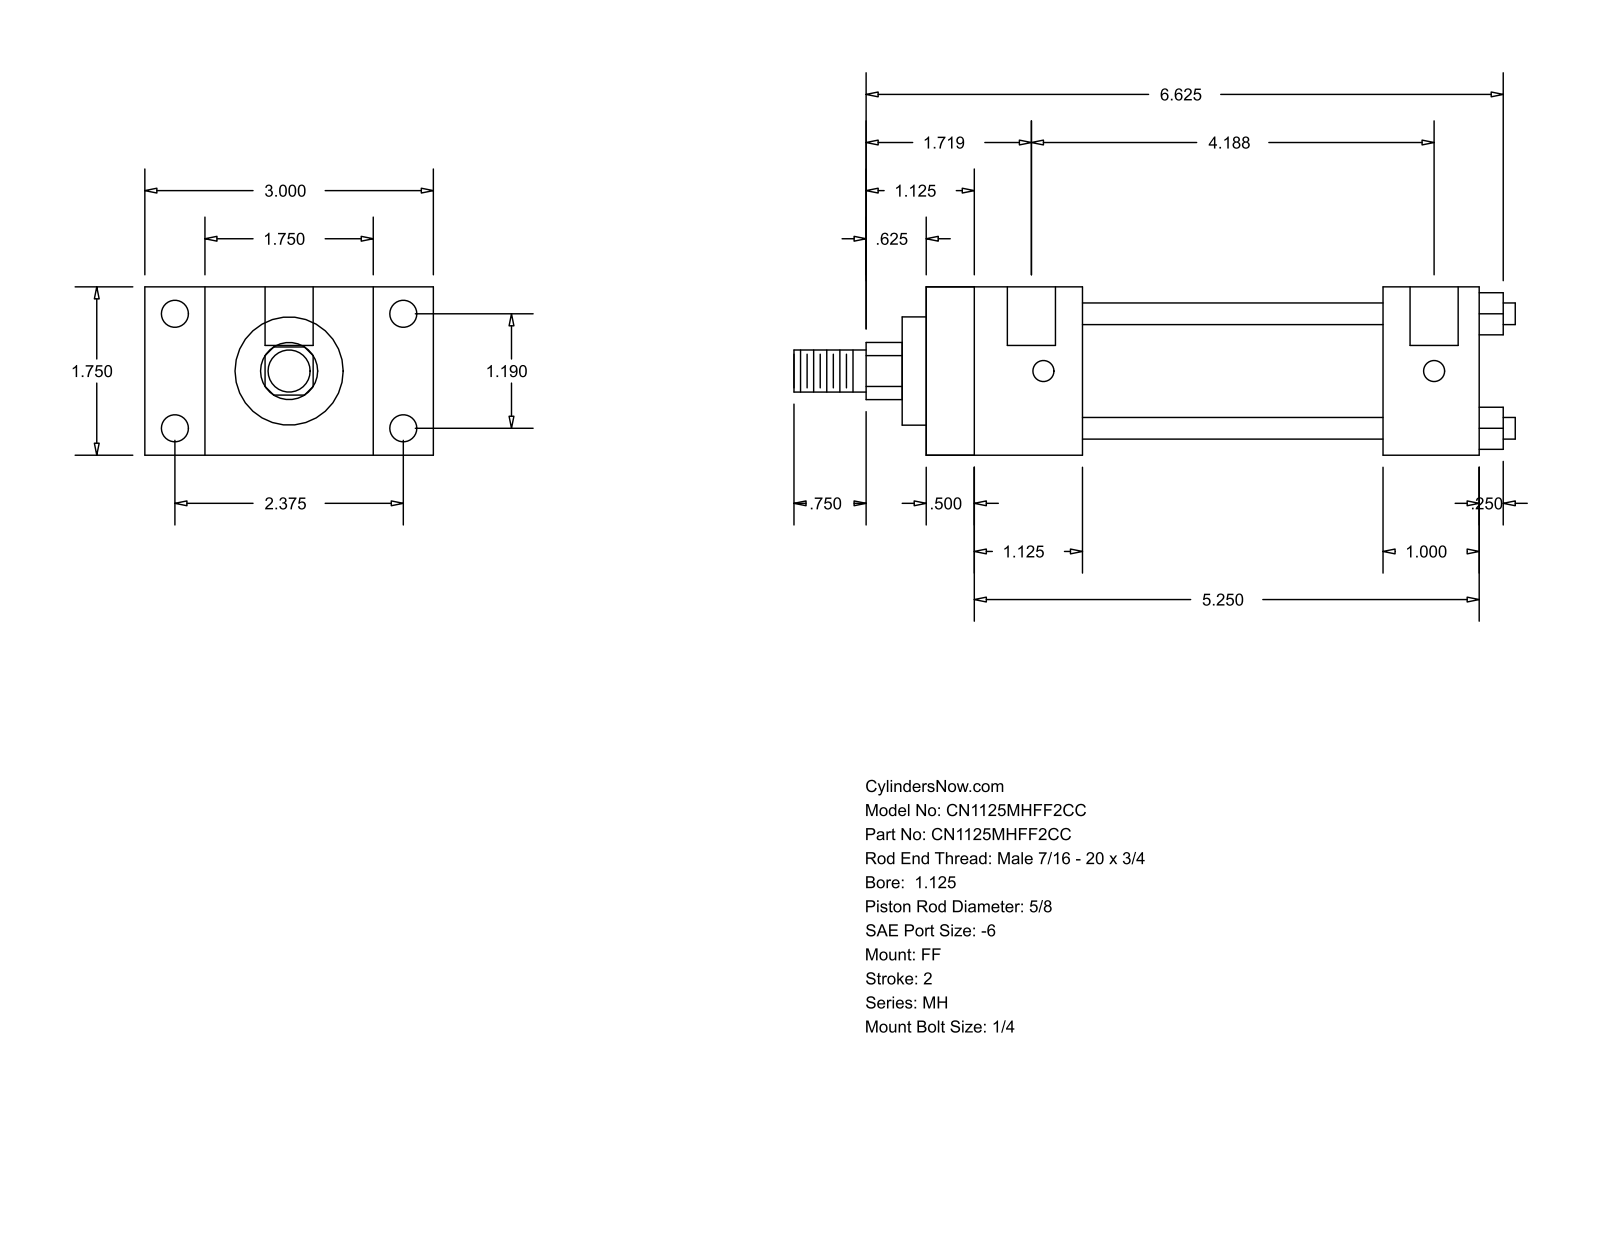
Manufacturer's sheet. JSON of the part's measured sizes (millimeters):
{"part_name": "MH_FF__0112_0.625", "step_written_by": "GSSL Pune (CONFIG_CONTROL_DESIGN)", "units": "millimeters", "bodies": {"solids": 0, "faces": 92, "planar": 64, "cylindrical": 28, "other": 0}, "overall_size": [190.5, 76.2, 44.45], "round_holes": [[5.56, 4], [7.14, 4], [12.7, 2]], "round_bosses_or_shafts": [[5.71, 4], [34.92, 1], [28.57, 1], [15.88, 1], [11.11, 1]], "partial_cylinders_radius": [[7.54, 1]], "face_to_face_distances": [44.46, 146.05, 12.69, 133.36, 15.87, 28.58, 60.33, 25.4, 41.27, 120.65], "hole_center_spacings": [30.22, 60.32, 67.47, 103.19, 3.17, 106.36]}
